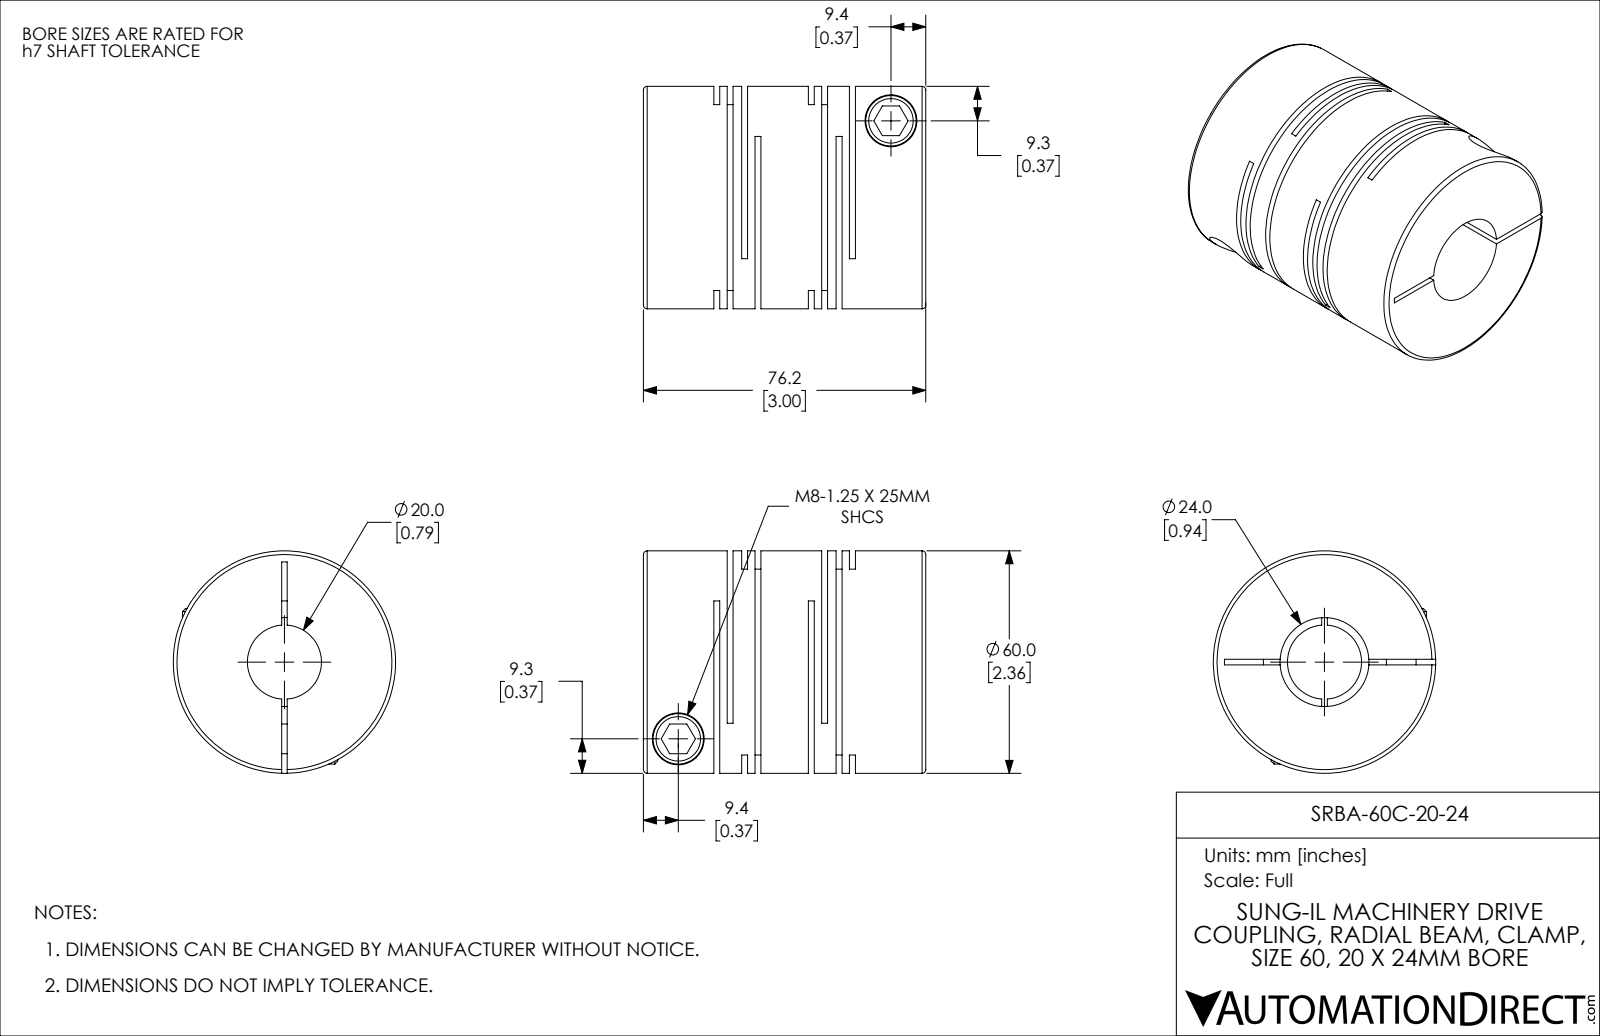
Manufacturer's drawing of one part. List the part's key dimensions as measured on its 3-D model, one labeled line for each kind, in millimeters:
Part name (STEP PRODUCT): SRBA-60C-20-24
STEP written by: SolidWorks 2021 (CONFIG_CONTROL_DESIGN)
Units: millimetres
Bodies: 1 solid, 115 faces (60 planar, 42 cylindrical, 13 other)
Overall size (bounding box): 76.2 × 60 × 60
Volume: 154 300 mm³ · Surface area: 57 330 mm²
Round holes (diameter × count): ⌀8 ×2, ⌀14 ×2, ⌀20 ×1, ⌀24 ×1
Round bosses / shafts (diameter × count): ⌀13.6 ×2, ⌀60 ×1
Main face-to-face distances: 1.6, 3.6, 7.5, 25.5, 33, 27.1, 5.9, 23.9, 18, 2
